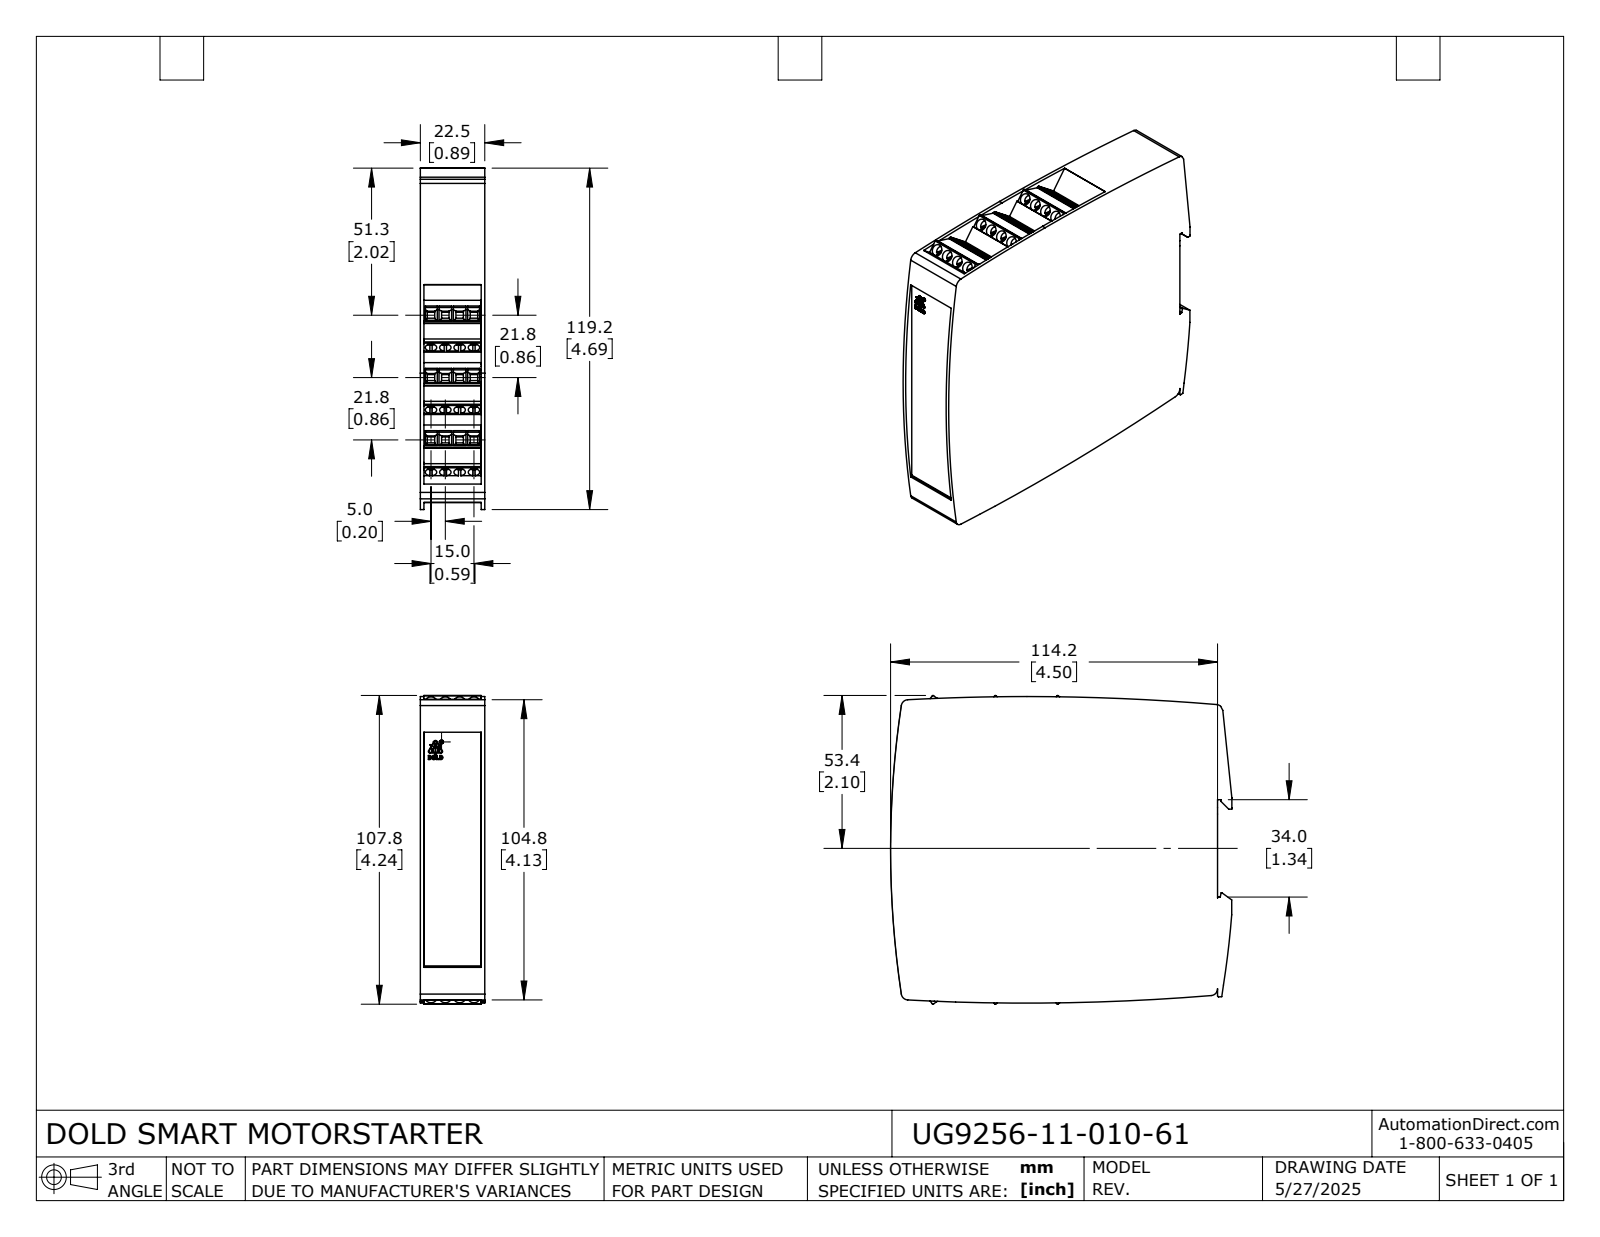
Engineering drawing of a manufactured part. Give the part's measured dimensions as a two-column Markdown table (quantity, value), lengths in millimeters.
| quantity | value |
| --- | --- |
| part name | UG9256-11-010-61 |
| STEP written by | SolidWorks 2024 (AUTOMOTIVE_DESIGN) |
| units | millimeters |
| bodies | 1 solid, 1036 faces (813 planar, 222 cylindrical, 1 other) |
| overall size | 119.2 × 107.8 × 22.5 |
| volume | 259 700 mm³ |
| surface area | 41 750 mm² |
| round holes (diameter × count) | 4 × 24, 1.3 × 1 |
| round bosses / shafts (diameter × count) | 3.8 × 24, 1.2 × 1 |
| partial cylindrical surfaces (radius × count) | 0.3 × 15, 0.5 × 14, 0.1 × 12, 2.4 × 7, 0.1 × 6, 0.1 × 4, 800 × 4, 0.5 × 3 |
| main face-to-face distances | 22.5, 1.2, 21.3, 17.1, 111.2, 1.3, 21.2, 34.3, 13.4, 19.9 |
| hole center spacings | 14.3, 5, 13.4, 16.7, 10, 27.3, 20.1, 26.8 |
